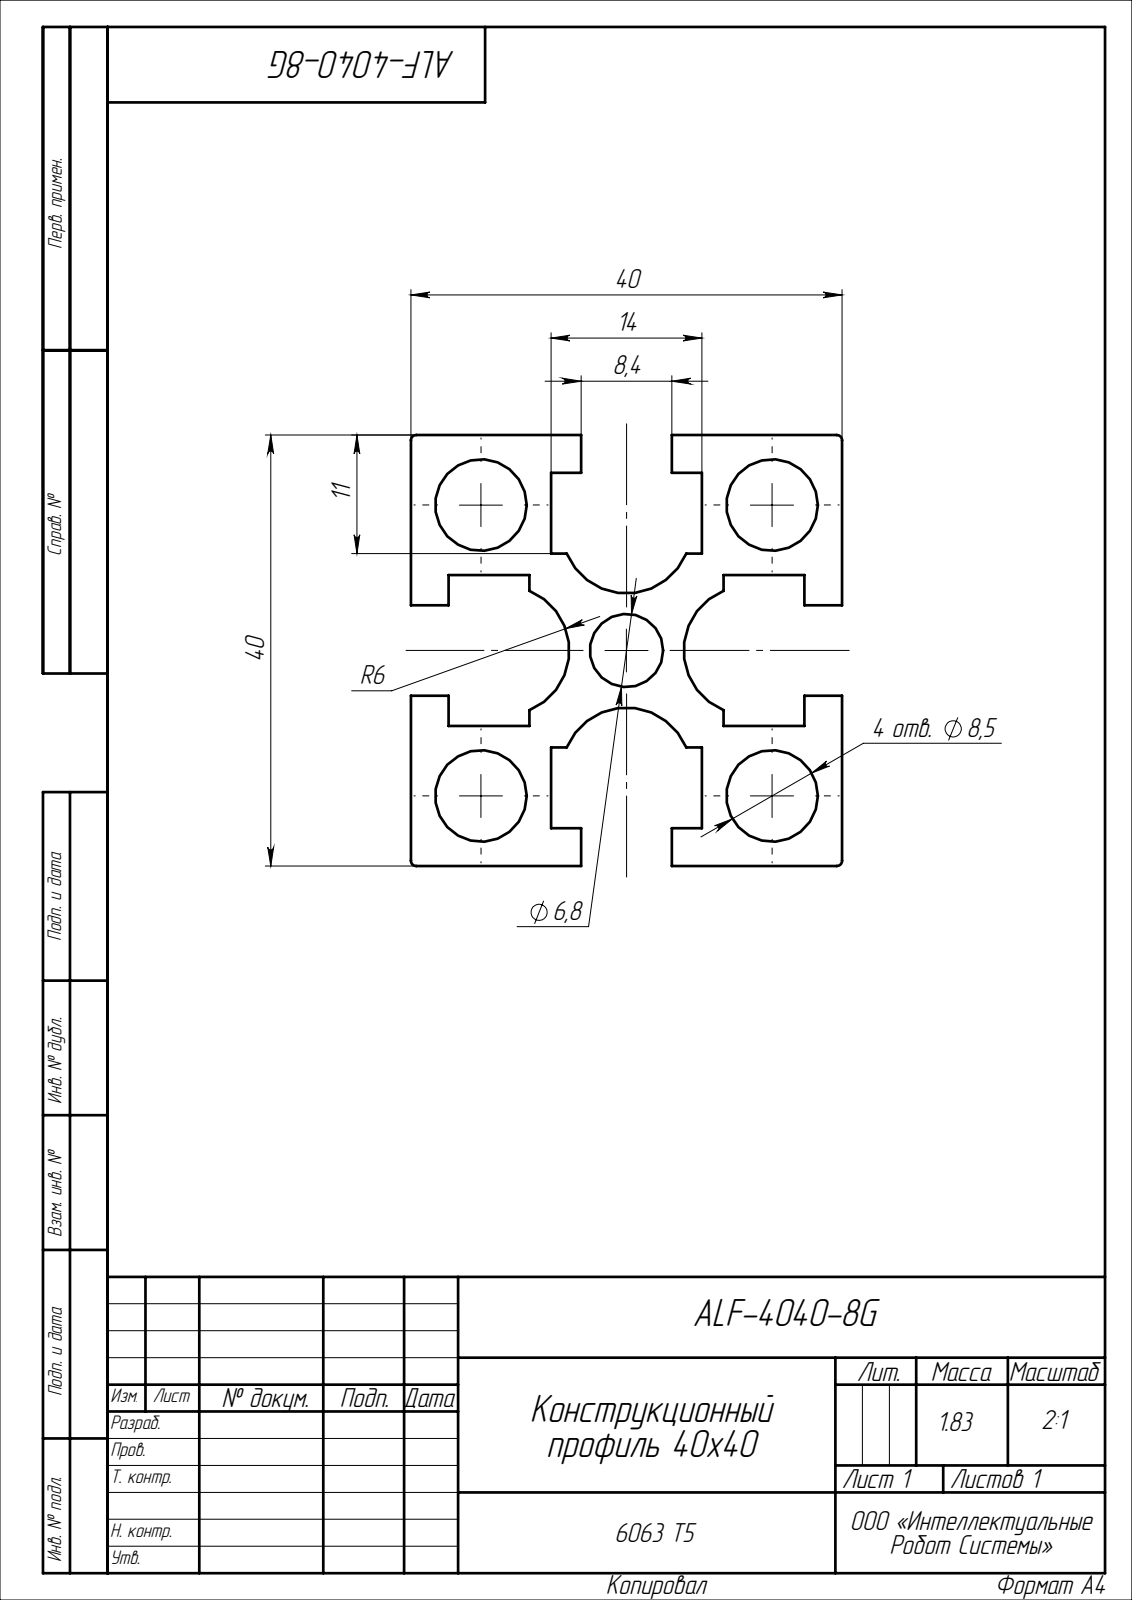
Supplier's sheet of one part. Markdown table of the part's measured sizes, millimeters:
| quantity | value |
| --- | --- |
| part name | ALF-4040-8G |
| STEP written by | SolidWorks 2022 (CONFIG_CONTROL_DESIGN) |
| units | millimeters |
| bodies | 1 solid, 61 faces (42 planar, 19 cylindrical, 0 other) |
| overall size | 1000 × 40 × 40 |
| volume | 680 327 mm³ |
| surface area | 433 661 mm² |
| round holes (diameter × count) | 8.5 × 4, 6.8 × 1 |
| partial cylindrical surfaces (radius × count) | 0.5 × 4, 6 × 4 |
| main face-to-face distances | 40, 13, 27, 14, 15.8, 24.2, 2.8, 11.2, 3.5, 36.5 |
| hole center spacings | 19.09, 27, 38.18 |
